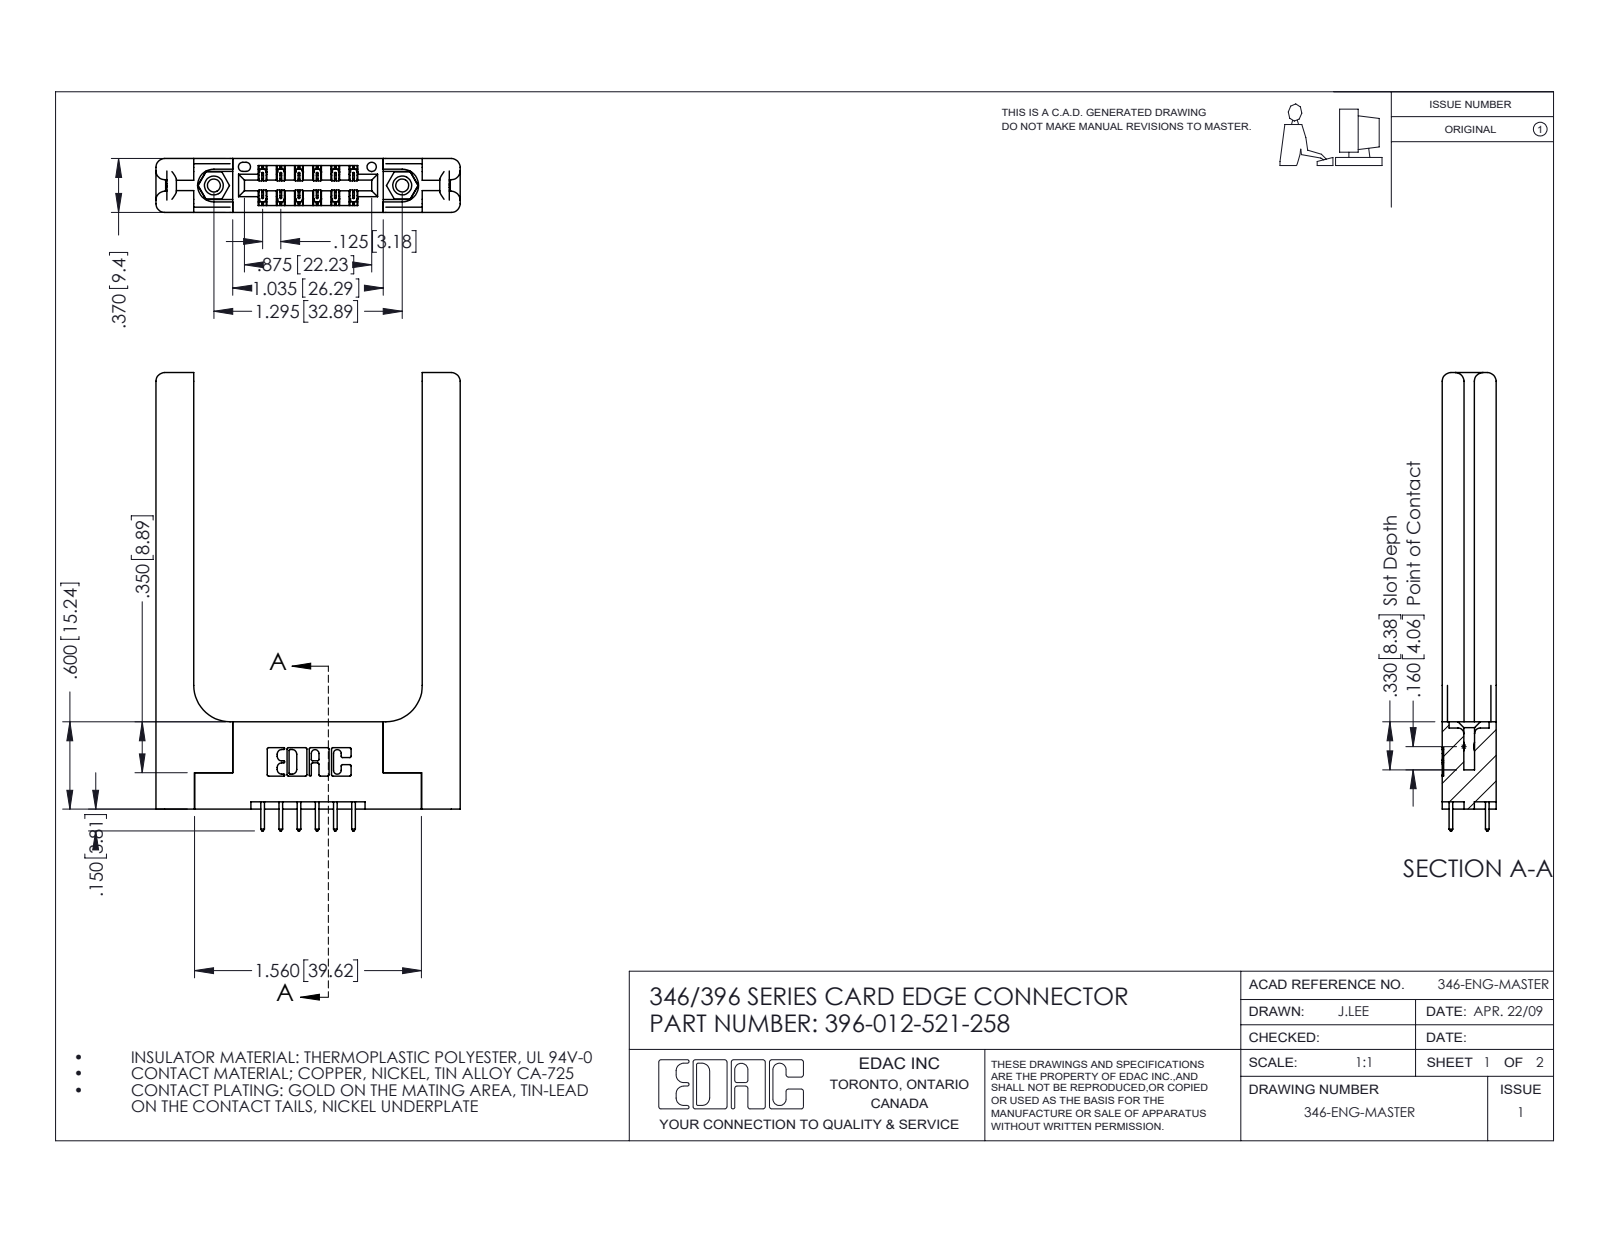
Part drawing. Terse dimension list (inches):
name: 346 Part_Flush Mounting Lugs - 0.156 Dia-TH; 346-220-058_345-220-058; 396-012-521-258; 345-250-001_345-250-001-102 (+1 more)
written by: SolidWorks 2016 (CONFIG_CONTROL_DESIGN)
unit: in
bodies: 17 solids, 1002 faces (644 planar, 298 cylindrical, 60 other)
size: 3.15 × 2.091 × 0.37
volume: 0.756 in³; area: 17.21 in²
holes: 2× ⌀0.089, 2× ⌀0.125, 2× ⌀0.156, 1× ⌀0.064
bosses: 2× ⌀0.155
rounds: 22× R0.01, 18× R0.006, 16× R0.06, 12× R0.01, 6× R0.007, 6× R0.031, 3× R0.026, 2× R0.014
face distances: 0.37, 0.15, 0.22, 0.25, 0.072, 0.148, 1.571, 0.102, 0.048, 0.322
hole spacings: 0.246, 1.092, 1.295
